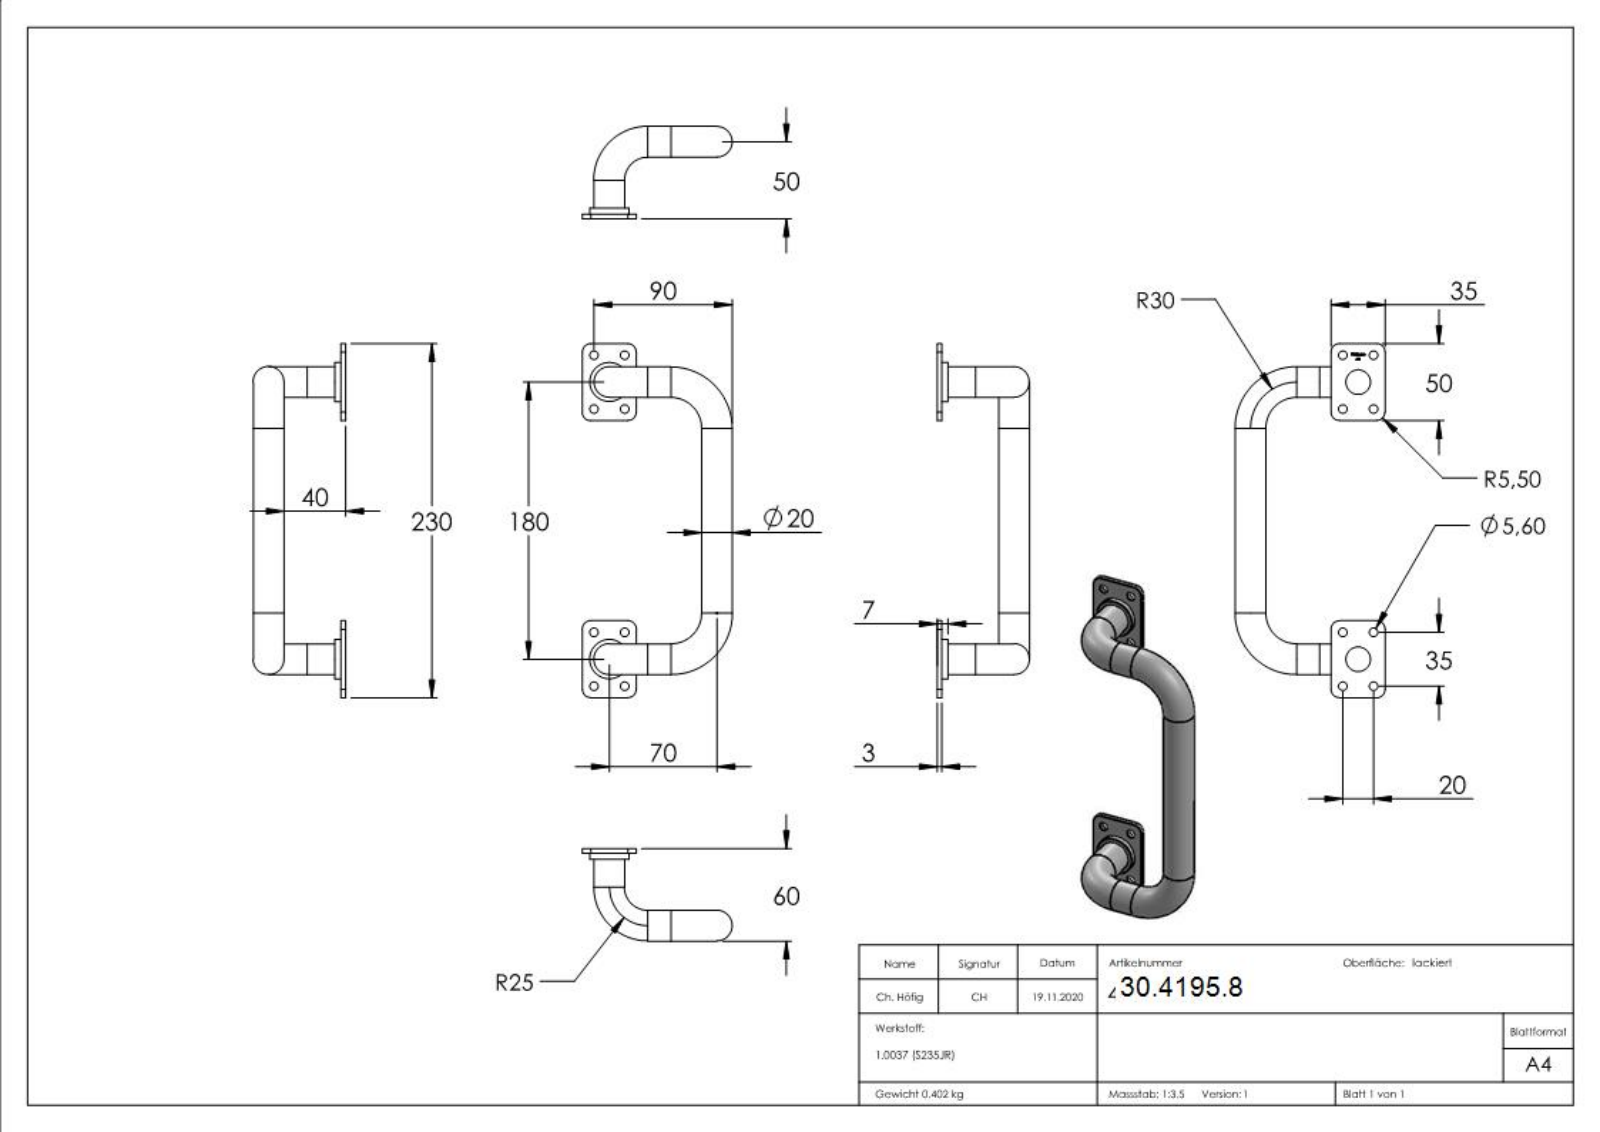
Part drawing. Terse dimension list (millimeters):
name: 491
written by: SolidWorks 2018 (CONFIG_CONTROL_DESIGN)
unit: mm
bodies: 1 solid, 227 faces (106 planar, 48 cylindrical, 73 other)
size: 230 × 97.5 × 60
volume: 51 601 mm³; area: 48 786 mm²
holes: 8× ⌀5.6, 5× ⌀16
bosses: 5× ⌀20, 2× ⌀25.5
rounds: 8× R5.5
face distances: 3, 7, 4, 35, 50, 180, 130, 230, 2.9, 6.9
hole spacings: 20.16, 180, 20, 35, 40.31, 162.81, 181.11, 197.75
